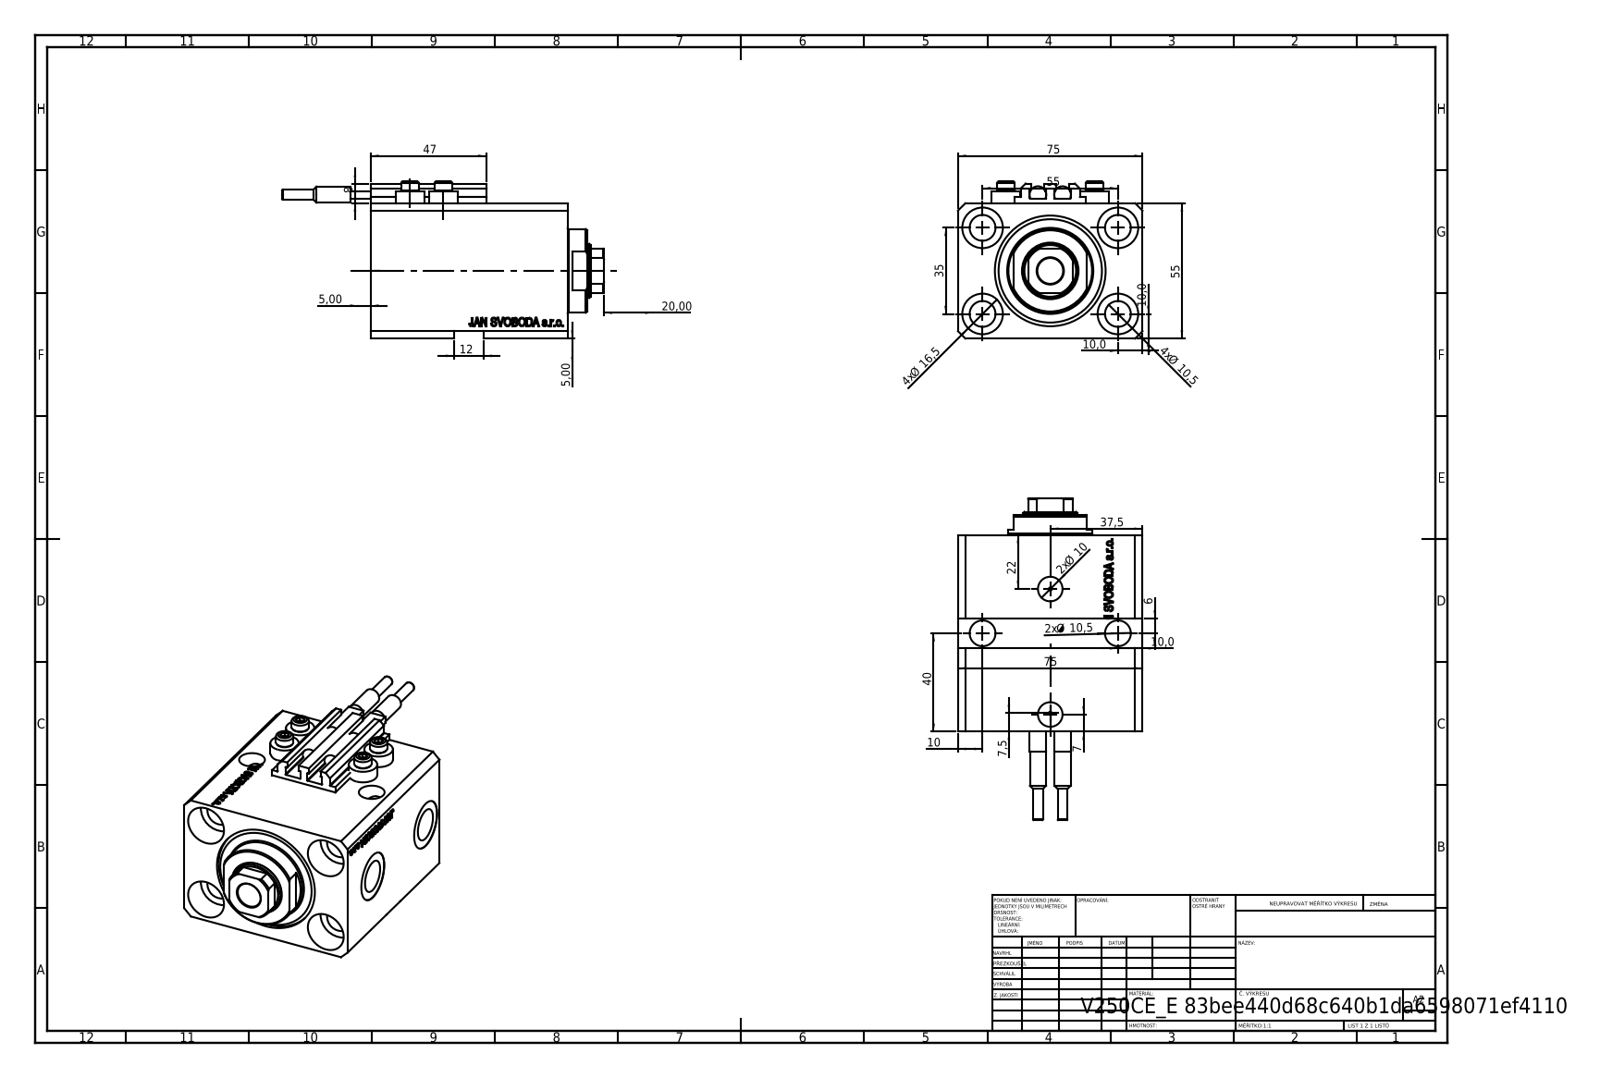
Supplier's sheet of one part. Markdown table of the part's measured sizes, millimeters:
| quantity | value |
| --- | --- |
| part name | ALLEN BOLT V250CE; V250CE_VC_E; SWITCH_V250CE; V250CE_C_VCP (+1 more) |
| STEP written by | SolidWorks 2019 (CONFIG_CONTROL_DESIGN) |
| units | millimeters |
| bodies | 10 solids, 1116 faces (546 planar, 138 cylindrical, 432 other) |
| overall size | 130.9 × 75 × 64 |
| volume | 287 445 mm³ |
| surface area | 79 816 mm² |
| round holes (diameter × count) | 10.5 × 7, 1.25 × 4, 4 × 4, 16.5 × 4, 10 × 2, 13.16 × 2, 20 × 2, 22 × 1, 32 × 1, 45 × 1 |
| round bosses / shafts (diameter × count) | 11.6 × 4, 7 × 4, 6.8 × 2, 6.5 × 2, 4 × 2, 34 × 1 |
| partial cylindrical surfaces (radius × count) | 0.2 × 10, 10.5 × 1 |
| main face-to-face distances | 55, 75, 3, 80, 52.9, 27.1, 9.9, 57, 43, 70.1 |
| hole center spacings | 32.6, 55, 13.6, 14.09, 19.89, 20.12, 25.81, 28.48 |
